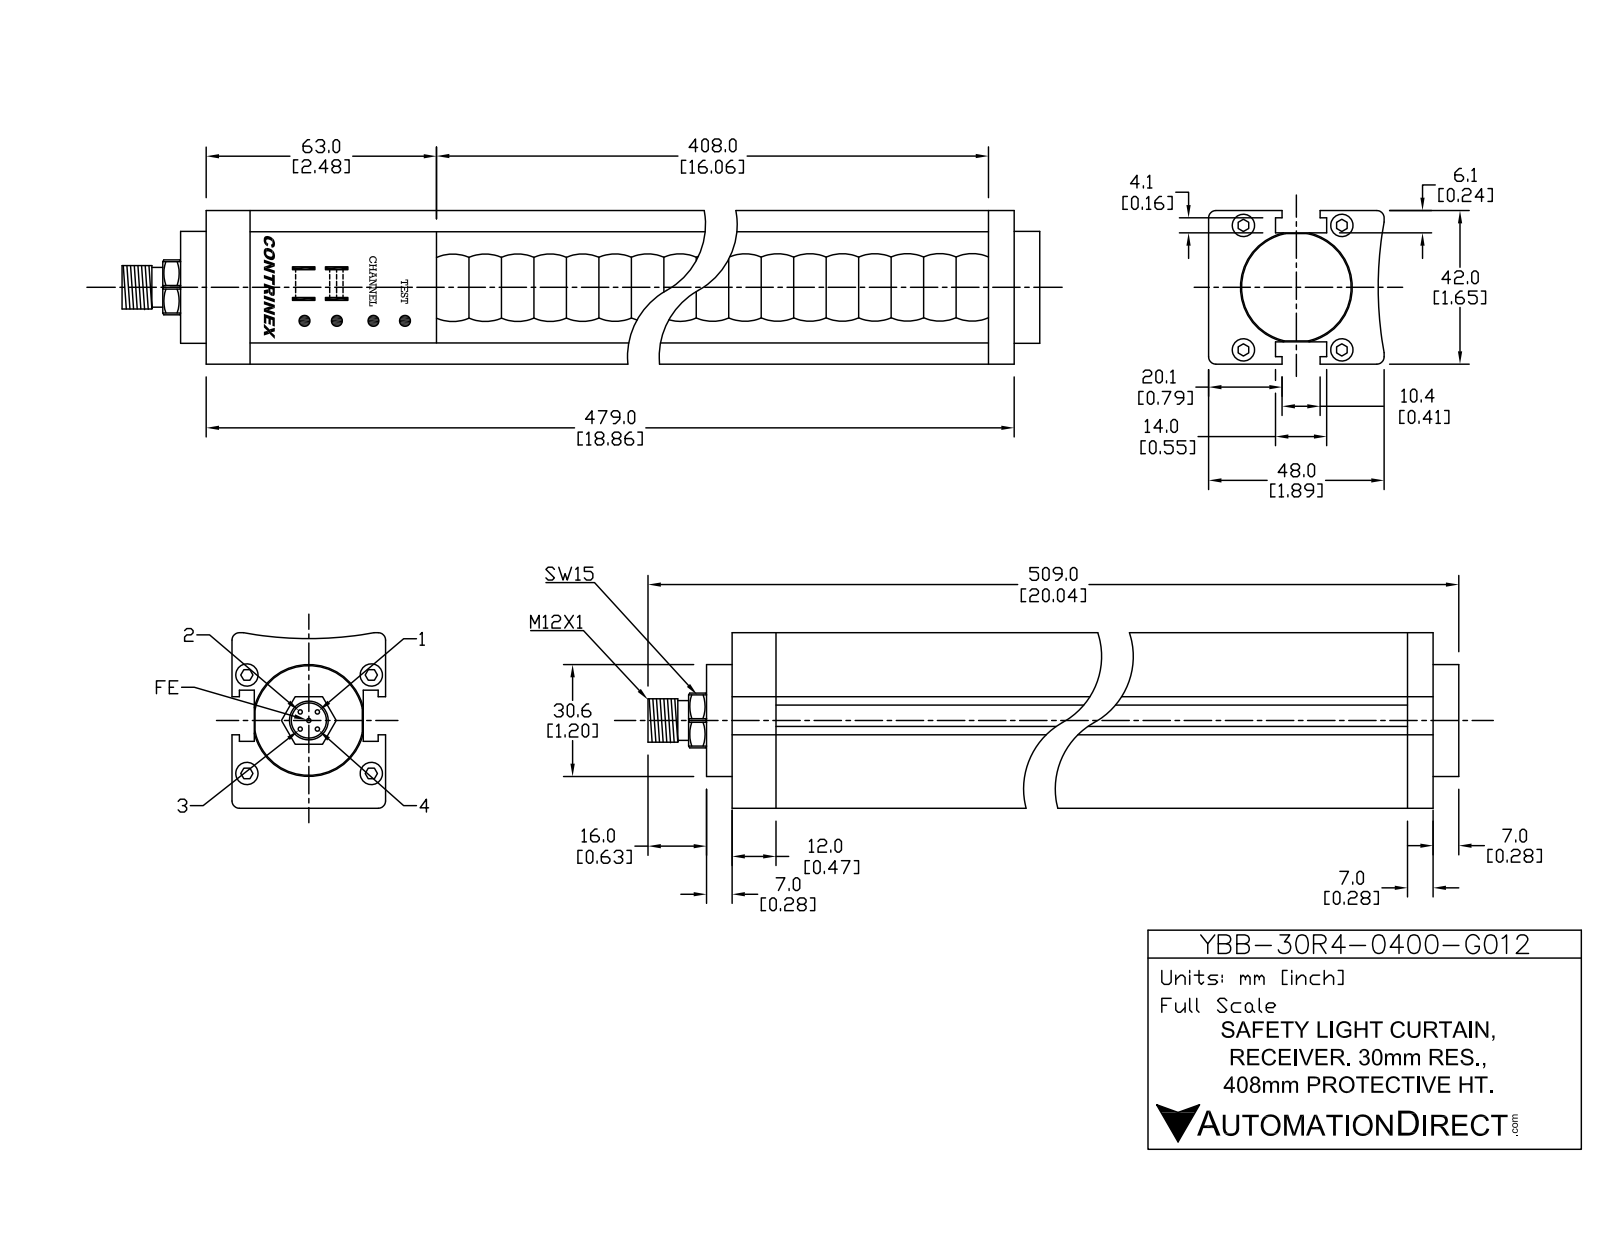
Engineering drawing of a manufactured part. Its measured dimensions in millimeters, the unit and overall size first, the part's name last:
Units: millimetres
Overall size (bounding box): 509 × 48 × 42
Round holes (diameter × count): ⌀6 ×4, ⌀8.5 ×1, ⌀32 ×1
Round bosses / shafts (diameter × count): ⌀1 ×5, ⌀5.5 ×4, ⌀30.6 ×1, ⌀12 ×1, ⌀10.5 ×1
Partial cylindrical surfaces — rounded edges, fillets, slot ends (radius × count): R1 ×48, R0.5 ×4, R0.55 ×2, R8.2 ×1, R100 ×1
Main face-to-face distances: 6.3, 35.7, 42, 29.4, 14, 17.2, 31.2, 459, 15.7, 29.7
Hole centre spacings: 21.04, 22.34, 26.9, 34, 43.35
Volume: 868 060 mm³ · Surface area: 119 957 mm²
Bodies: 19 solids, 440 faces (208 planar, 168 cylindrical, 64 other)
Part name (STEP PRODUCT): YBB-30R4-0400-G012
STEP written by: SolidWorks 2016 (AUTOMOTIVE_DESIGN)
